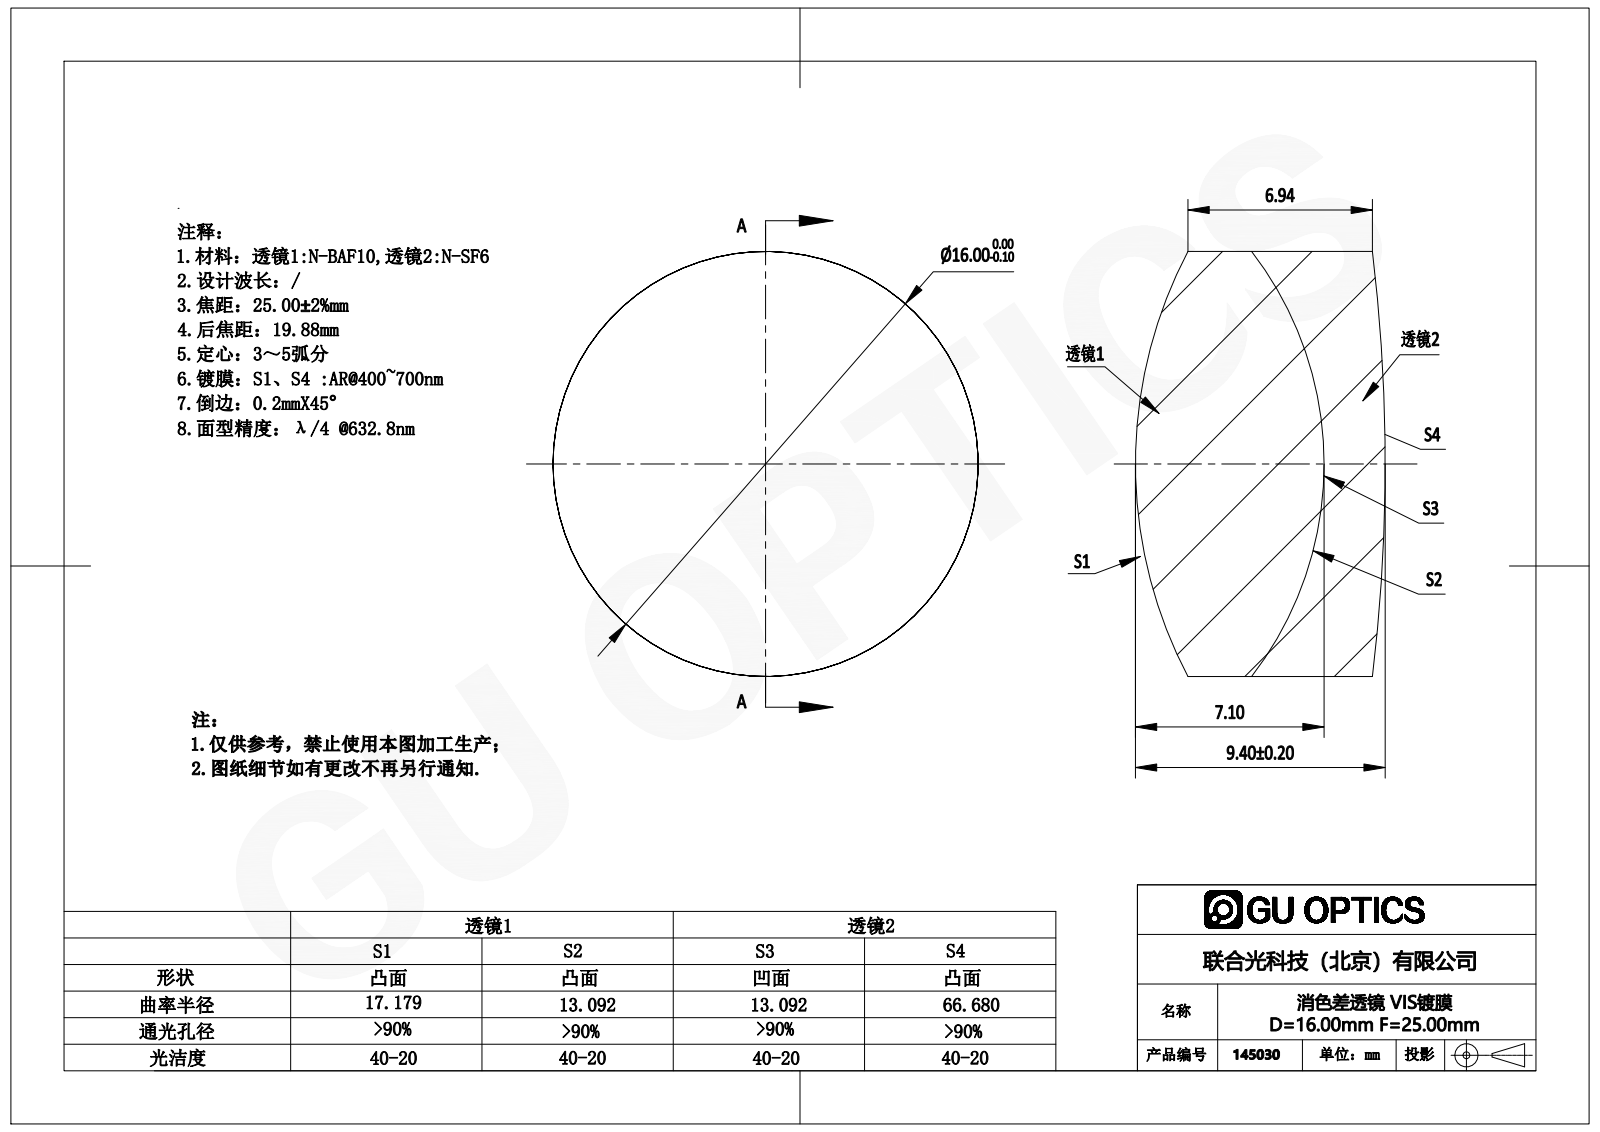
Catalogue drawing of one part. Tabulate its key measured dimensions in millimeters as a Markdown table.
| quantity | value |
| --- | --- |
| part name | 145030 |
| STEP written by | SolidWorks 2016 (AUTOMOTIVE_DESIGN) |
| units | millimeters |
| bodies | 2 solids, 12 faces (0 planar, 4 cylindrical, 8 other) |
| overall size | 16 × 16 × 9.4 |
| volume | 1 647 mm³ |
| surface area | 1 213 mm² |
| round bosses / shafts (diameter × count) | 16 × 1 |
